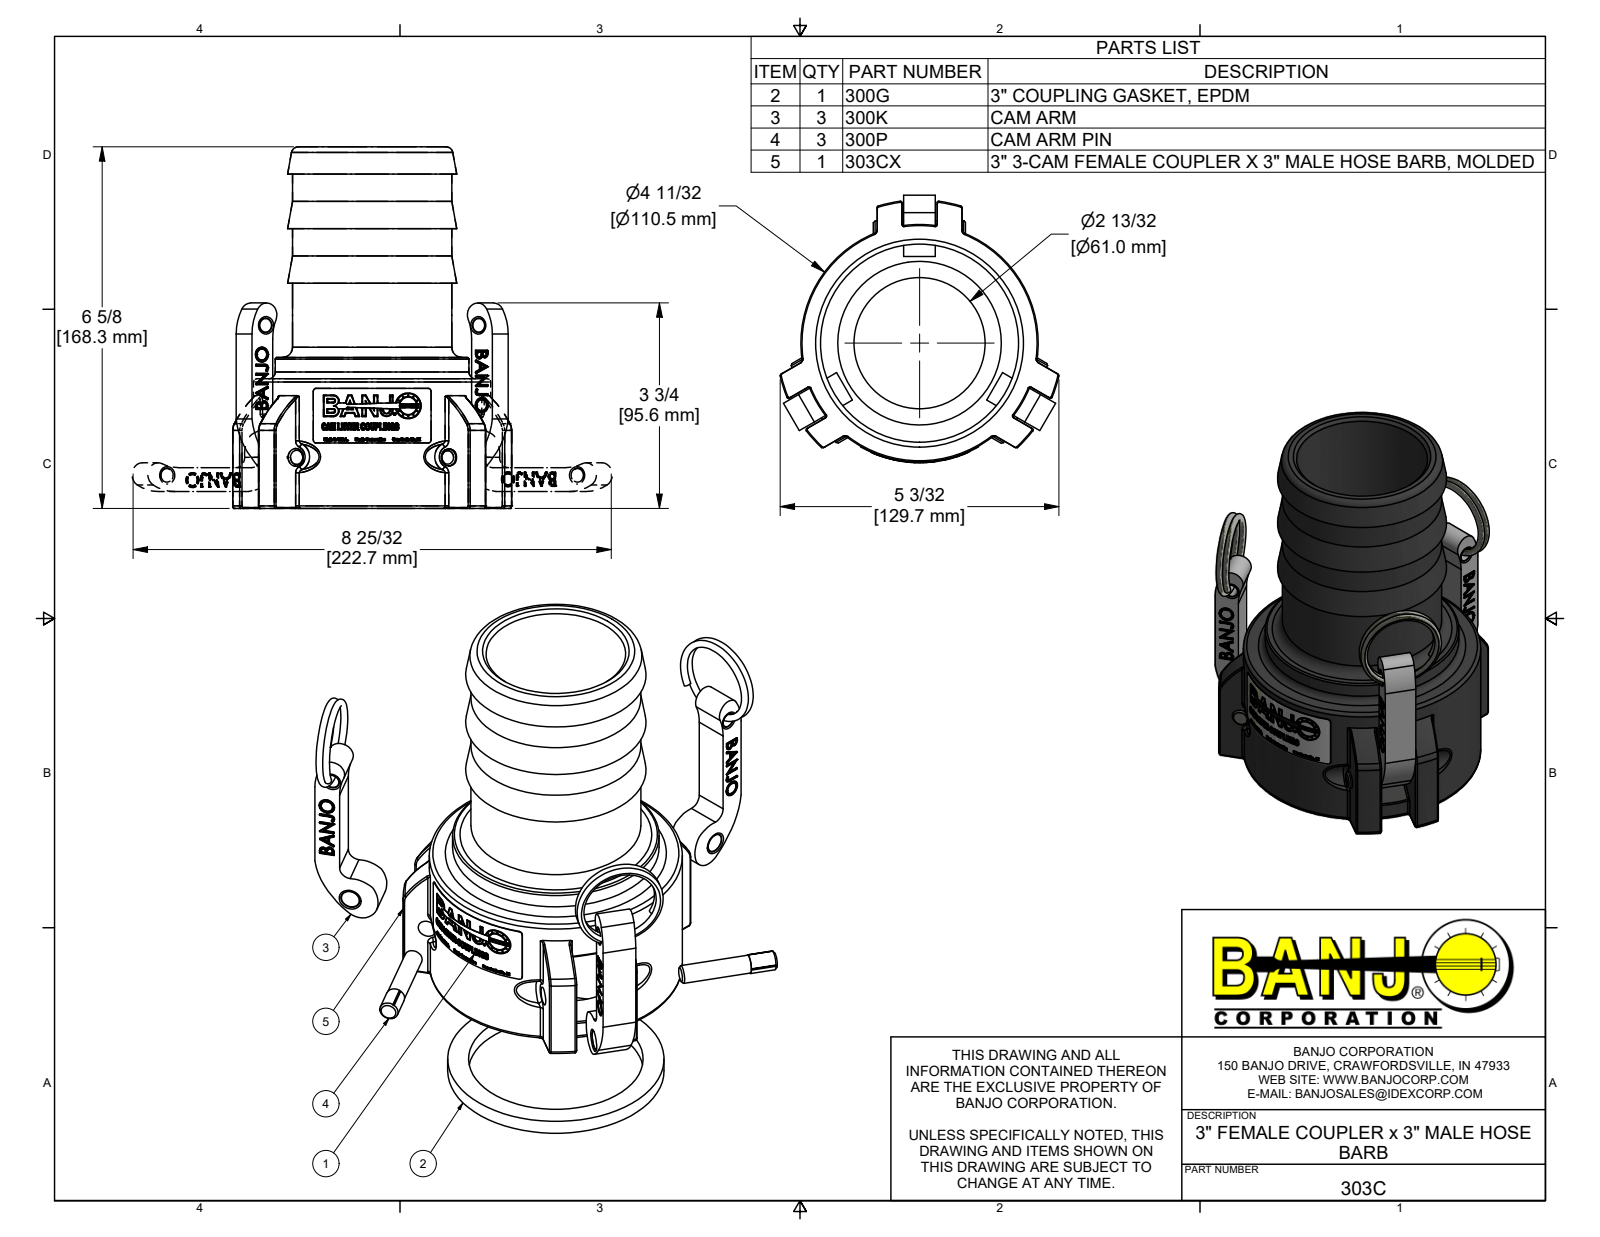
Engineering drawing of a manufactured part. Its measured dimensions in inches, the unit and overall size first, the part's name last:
Units: inches
Overall size (bounding box): 6.64 × 5.113 × 4.776
Round holes (diameter × count): ⌀0.313 ×3, ⌀0.318 ×1, ⌀0.449 ×1, ⌀2.4 ×1, ⌀3 ×1, ⌀3.63 ×1, ⌀3.8 ×1
Round bosses / shafts (diameter × count): ⌀4.35 ×1, ⌀3.55 ×1, ⌀2.92 ×1, ⌀0.473 ×1
Partial cylindrical surfaces — rounded edges, fillets, slot ends (radius × count): R0.03 ×42, R0.06 ×10, R0.25 ×3, R0.028 ×2, R0.039 ×2, R0.093 ×2, R0.104 ×2, R0.058 ×1
Main face-to-face distances: 0.46, 1.1, 2.045, 0.64, 2.375, 0.33, 1.56, 1, 2.767, 0.722
Volume: 24.47 in³ · Surface area: 169.4 in²
Bodies: 2 solids, 1532 faces (589 planar, 262 cylindrical, 681 other)
Part name (STEP PRODUCT): 303C; 303CX; 150(200)D-150
STEP written by: Autodesk Inventor 2022 (AUTOMOTIVE_DESIGN)
